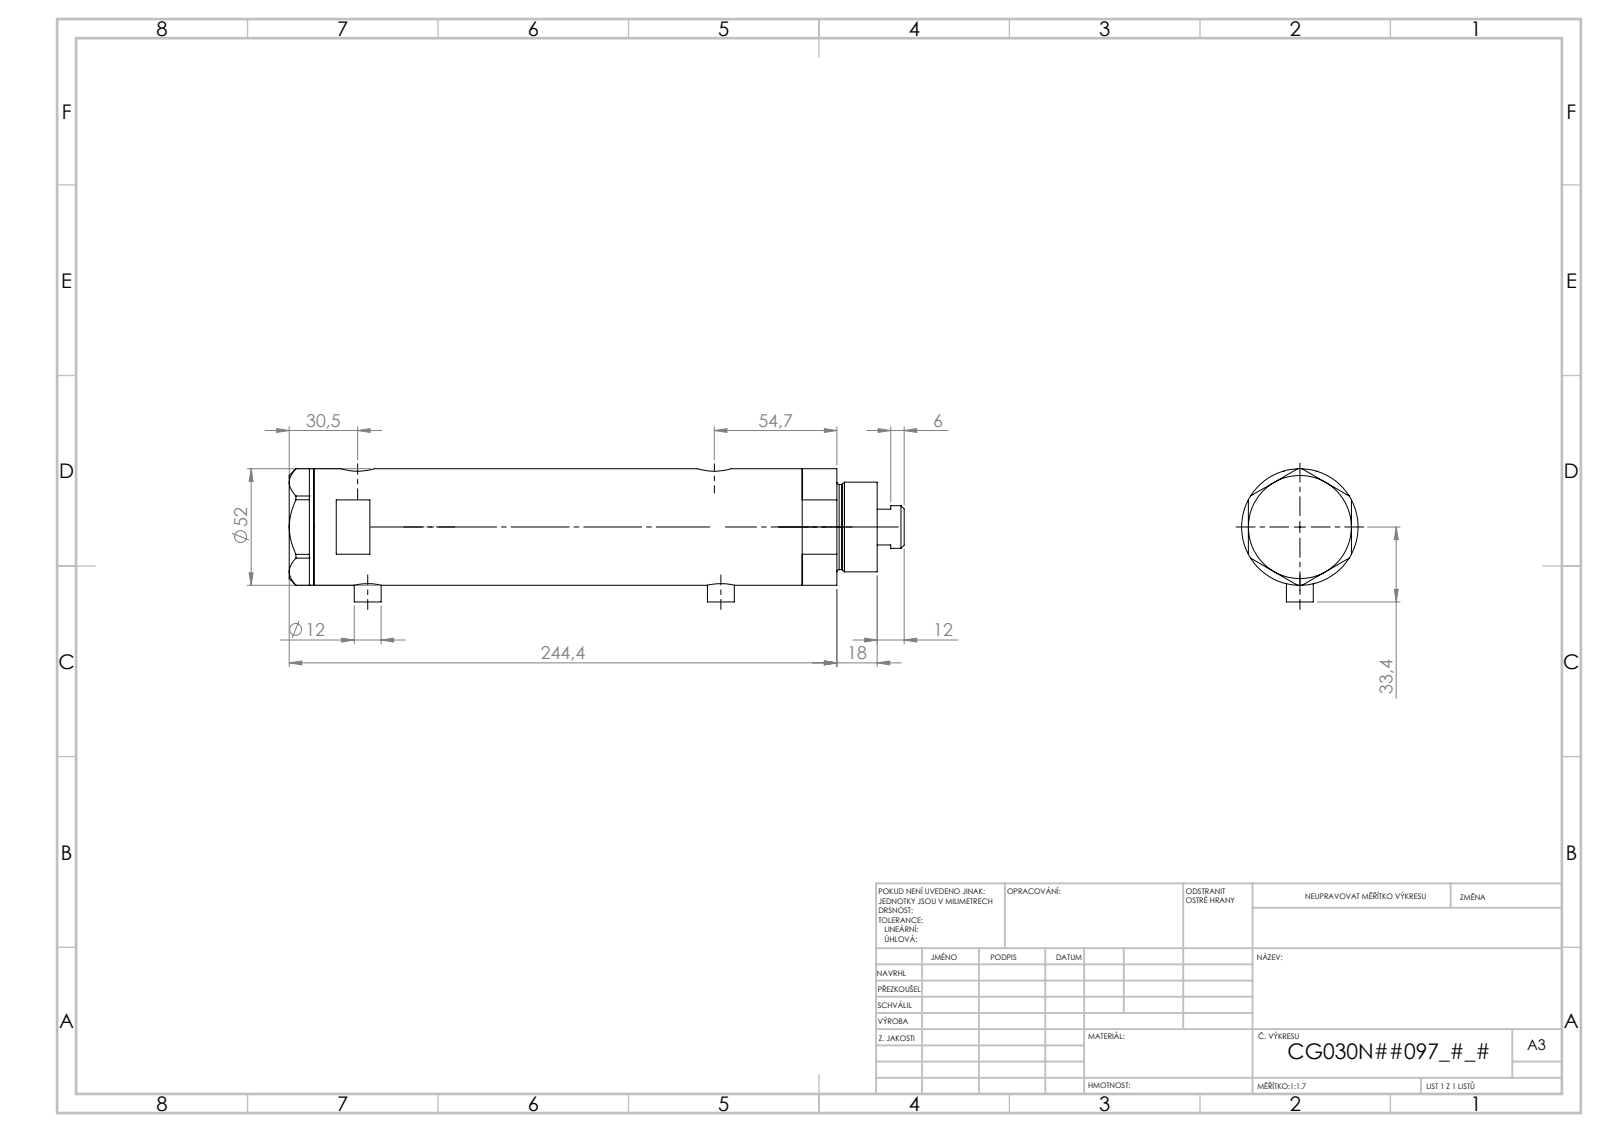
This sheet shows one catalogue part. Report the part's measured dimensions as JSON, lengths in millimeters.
{"part_name": "V270CG_FRONT; V270CG_MIDDLE; V270CG_BACK; V270CG_VC", "step_written_by": "SolidWorks 2019 (CONFIG_CONTROL_DESIGN)", "units": "millimeters", "bodies": {"solids": 4, "faces": 140, "planar": 67, "cylindrical": 53, "other": 20}, "overall_size": [246.02, 53.1, 52], "volume_mm3": 435427, "surface_area_mm2": 96172, "round_holes": [[5, 2], [9.73, 2], [12.5, 2], [15, 2], [6.5, 1], [20, 1], [21.5, 1], [30, 1], [33, 1], [44, 1]], "round_bosses_or_shafts": [[12, 2], [52, 1], [40, 1], [38, 1], [19, 1]], "face_to_face_distances": [150.54, 23.8, 126.74, 11, 34.8, 161.54, 46, 197.94, 186.94, 163.14], "hole_center_spacings": [2.9, 4.5, 123.75, 126.65, 128.25, 131.15, 2.89, 2.91]}
